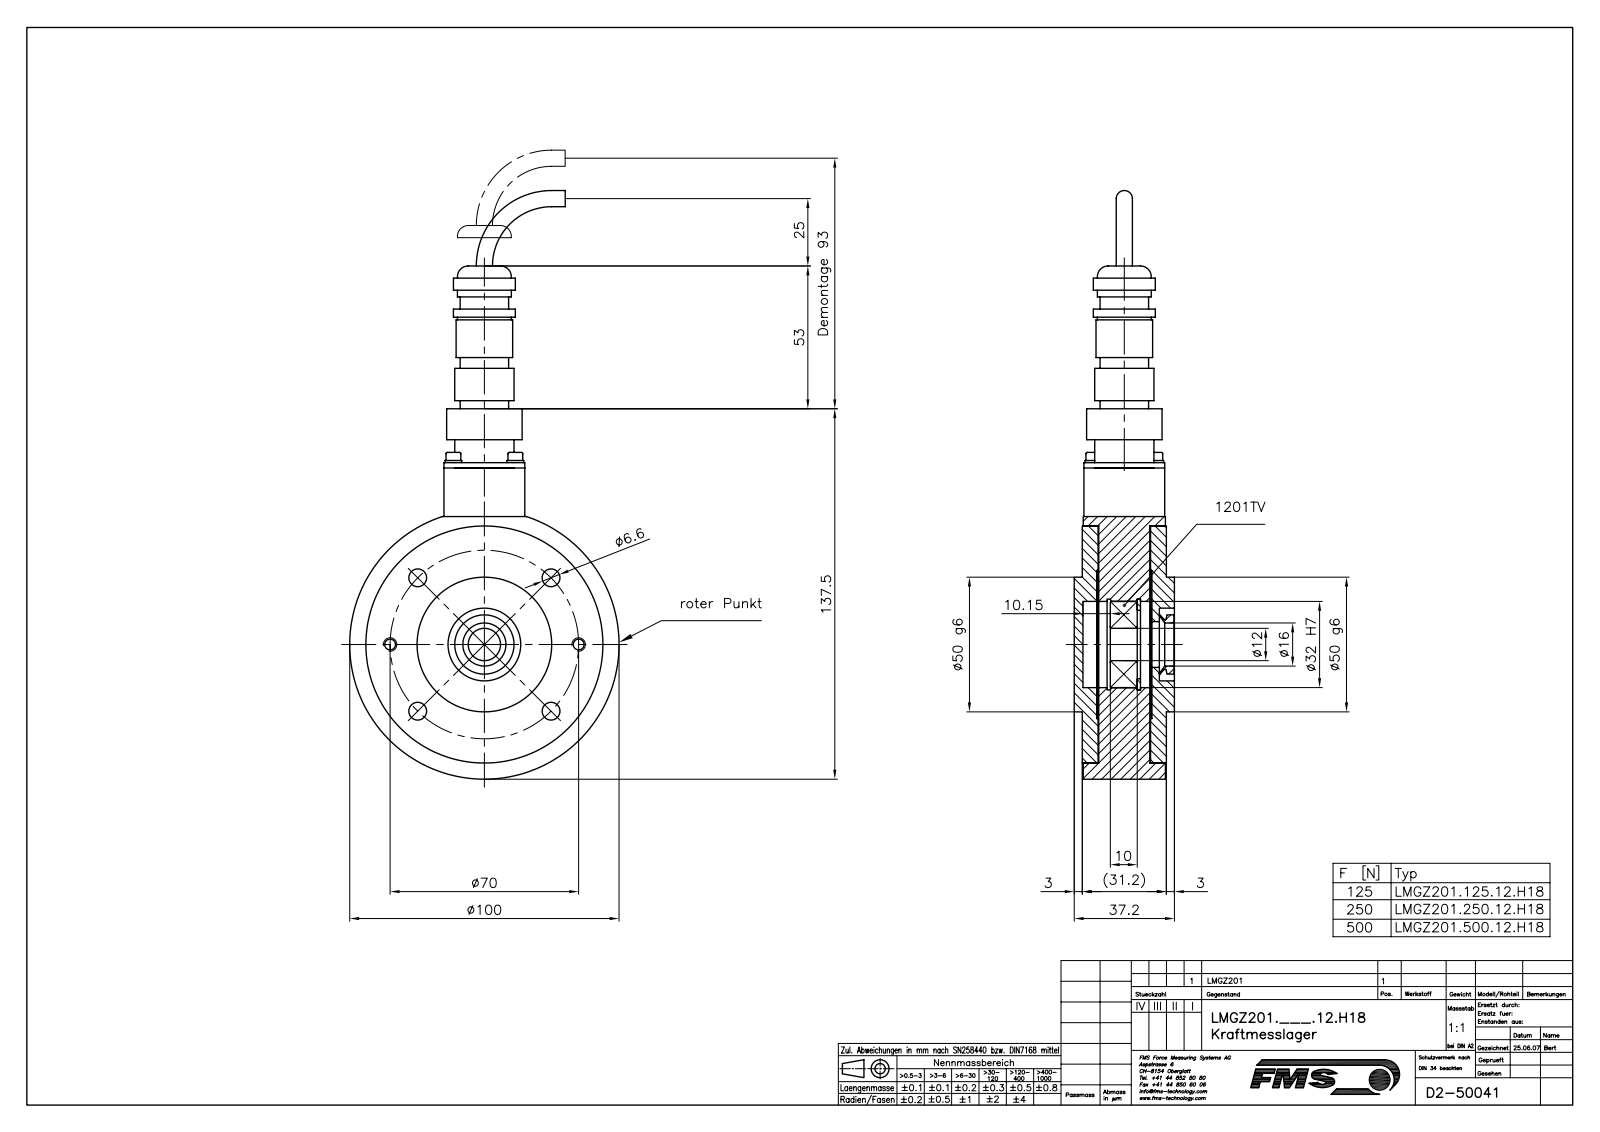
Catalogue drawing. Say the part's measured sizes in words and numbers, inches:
The part is named "L50041; L4866604; TEIL1; L48891 (+8 more)". Its 3-D file was written by "Mechanical Desktop 2007 (CONFIG_CONTROL_DESIGN)". It is 20 solids with 368 faces: 101 planar, 223 cylindrical and 44 other. Overall it measures 8.602 by 3.937 by 1.465 inches. Its volume is 16.63 cubic inches and its surface area 151.3 square inches. Round holes: 4 of diameter 0.102, 4 of diameter 0.126, 4 of diameter 0.134, 4 of diameter 0.26, 2 of diameter 0.157, 2 of diameter 0.217, 2 of diameter 0.394, 1 of diameter 0.472, 1 of diameter 0.63, 1 of diameter 0.669, 1 of diameter 1, 1 of diameter 1.063. Round bosses or shafts: 4 of diameter 0.244, 4 of diameter 0.217, 4 of diameter 0.118, 4 of diameter 0.098, 2 of diameter 0.866, 2 of diameter 0.315, 2 of diameter 0.197, 1 of diameter 3.937. Partial cylindrical surfaces (rounded edges, fillets, slot ends): 4 of radius 0.157. The main face-to-face distances are 0.758, 0.748, 0.23, 0.988, 0.24, 0.998, 0.768, 0.217, 0.787, 0.974. The hole center spacings are 1.378, 0.906, 1.055, 1.949, 2.546, 2.756, 1.281.
